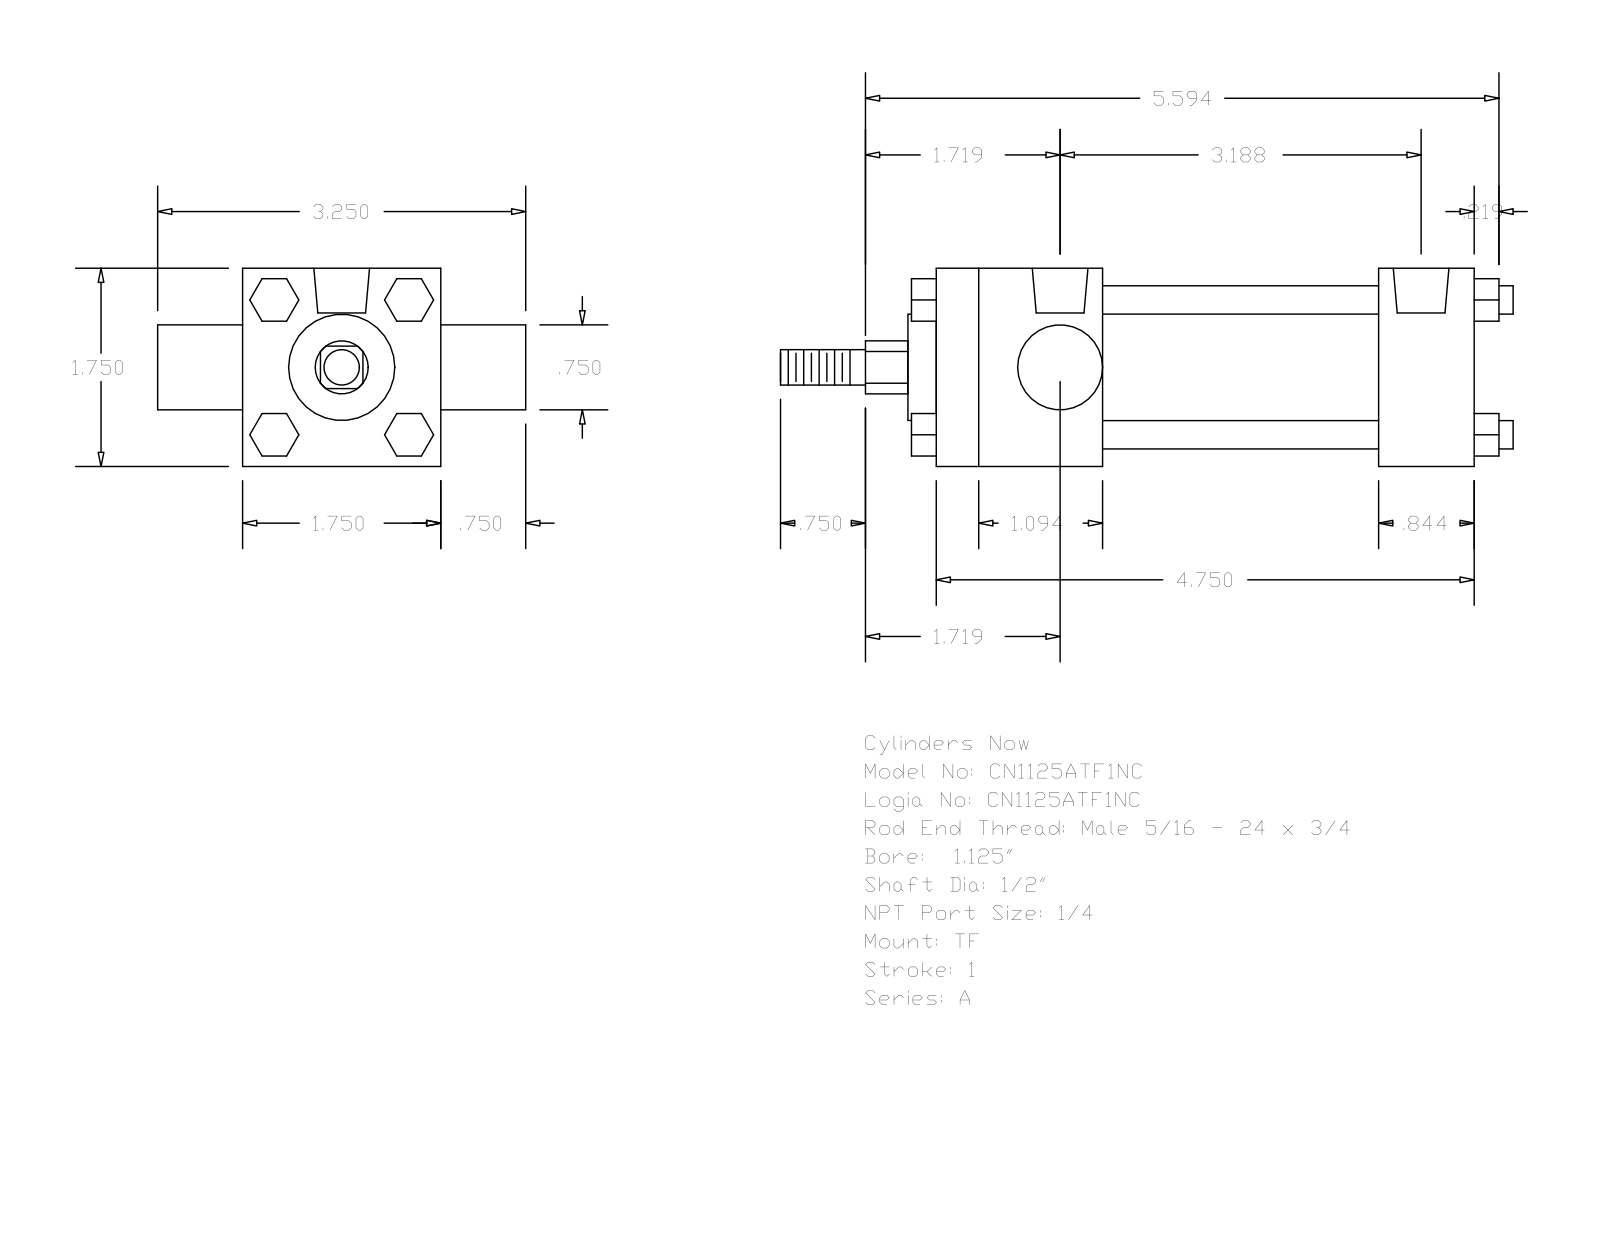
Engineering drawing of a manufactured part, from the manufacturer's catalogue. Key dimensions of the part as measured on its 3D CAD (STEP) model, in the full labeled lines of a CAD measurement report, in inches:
Part name (STEP PRODUCT): A_TF__0112_0.5
STEP written by: GSSL Pune (CONFIG_CONTROL_DESIGN)
Units: inches
Bodies: 0 solids, 120 faces (92 planar, 28 cylindrical, 0 other)
Overall size (bounding box): 6.469 × 3.25 × 1.75
Round holes (diameter × count): ⌀0.219 ×3, ⌀0.492 ×2
Round bosses / shafts (diameter × count): ⌀0.25 ×4, ⌀1.255 ×1, ⌀0.937 ×1, ⌀0.75 ×1, ⌀0.5 ×1, ⌀0.313 ×1
Partial cylindrical surfaces — rounded edges, fillets, slot ends (radius × count): R0.234 ×1
Main face-to-face distances: 1.75, 4.75, 3.906, 0.844, 1.469, 2.437, 3.281, 0.75, 2.5, 0.375
Hole centre spacings: 0.062, 0.063, 3.063, 3.125, 3.125, 3.187
